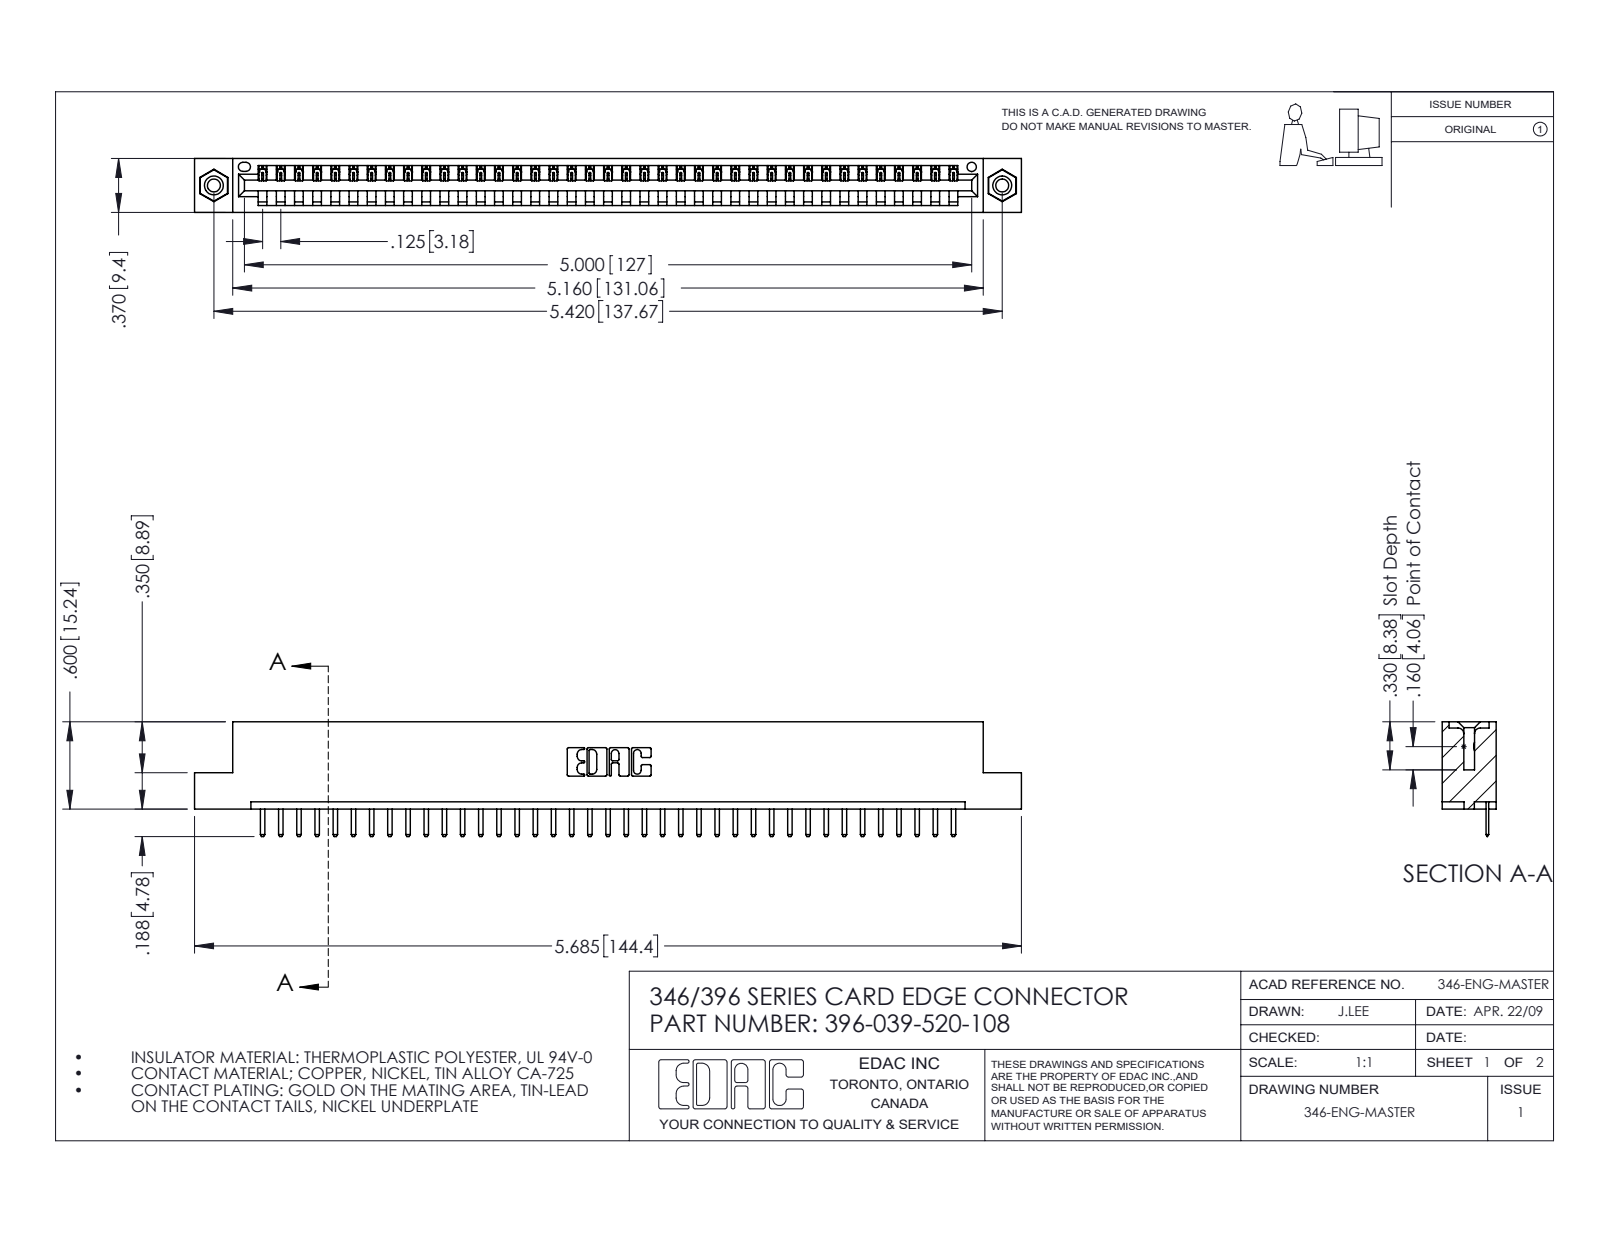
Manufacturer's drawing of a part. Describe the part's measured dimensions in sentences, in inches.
The part is named "396-039-520-108; 345-250-001_345-250-003-102; 345-292-001_345-293-120; 346 Part_Flush Mounting Lugs - 0.156 Dia-TI". Its 3-D file was written by "SolidWorks 2016 (CONFIG_CONTROL_DESIGN)". It is 42 solids with 2600 faces: 1746 planar, 838 cylindrical and 16 other. Overall it measures 5.685 by 0.788 by 0.37 inches. Its volume is 0.835 cubic inches and its surface area 25.91 square inches. Round holes: 2 of diameter 0.089, 2 of diameter 0.125, 2 of diameter 0.156, 1 of diameter 0.064. Round bosses or shafts: 2 of diameter 0.155. Partial cylindrical surfaces (rounded edges, fillets, slot ends): 80 of radius 0.01, 78 of radius 0.006, 22 of radius 0.01, 6 of radius 0.007, 6 of radius 0.031, 3 of radius 0.026, 2 of radius 0.031, 2 of radius 0.04. The main face-to-face distances are 0.048, 0.322, 0.37, 0.25, 0.148, 0.222, 0.1, 0.174, 0.072, 0.298. The hole center spacings are 0.246, 5.211, 5.42.
